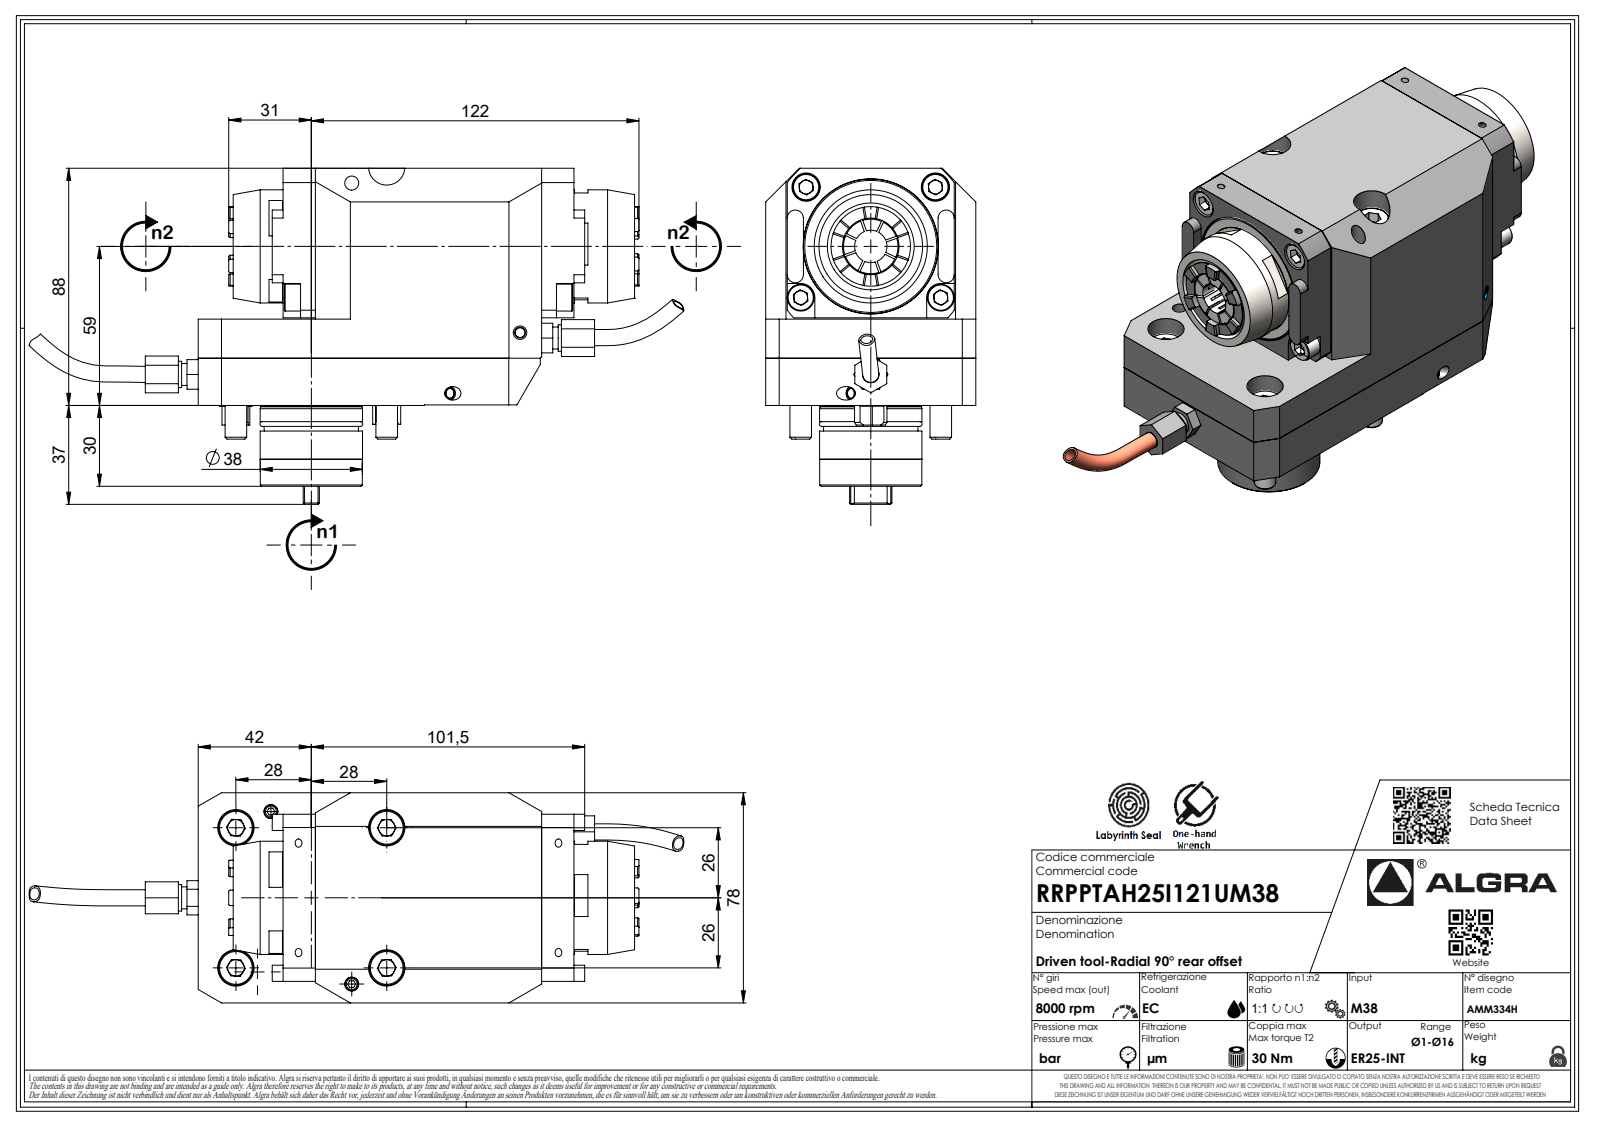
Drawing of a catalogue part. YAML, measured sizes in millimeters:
part_name: "RRPPTAH25I121UM38"
step_written_by: "SolidWorks 2023 (AUTOMOTIVE_DESIGN)"
units: millimeters
bodies: {solids: 1, faces: 557, planar: 384, cylindrical: 66, other: 107}
overall_size: [243.1, 124.7, 78]
volume: 836355
surface_area: 68296
round_holes:
  - {diameter: 2.1, count: 1}
round_bosses_or_shafts:
  - {diameter: 8, count: 4}
  - {diameter: 9.8, count: 2}
  - {diameter: 8.15, count: 2}
  - {diameter: 42, count: 1}
  - {diameter: 38, count: 1}
  - {diameter: 37.6, count: 1}
  - {diameter: 35, count: 1}
  - {diameter: 12, count: 1}
partial_cylinders:
  - {radius: 0.33, count: 7}
  - {radius: 0.52, count: 7}
  - {radius: 3.7, count: 7}
  - {radius: 3, count: 4}
  - {radius: 0.21, count: 1}
  - {radius: 6, count: 1}
  - {radius: 7.85, count: 1}
  - {radius: 25.1, count: 1}
face_to_face_distances: [78, 88, 56, 32, 31.8, 87.8, 8, 70, 62, 108]
